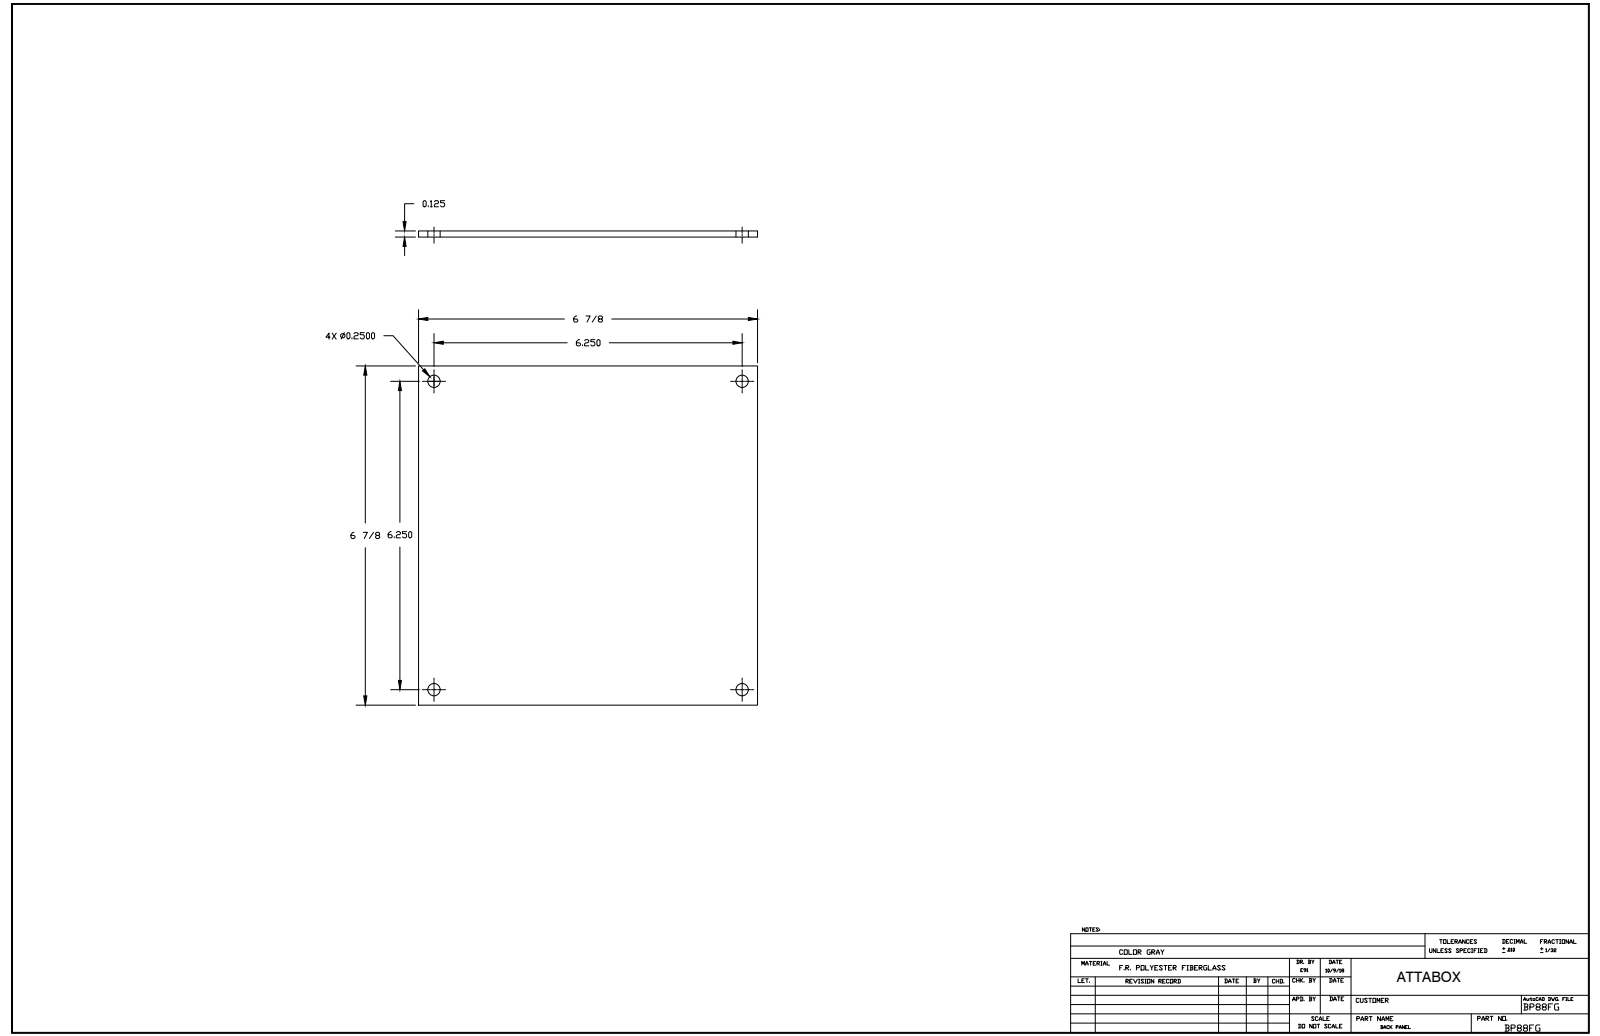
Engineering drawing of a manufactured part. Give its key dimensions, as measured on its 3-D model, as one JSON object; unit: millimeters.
{"part_name": "BP88FG_STP", "step_written_by": "Autodesk Inventor 2014 (AUTOMOTIVE_DESIGN)", "units": "millimeters", "bodies": {"solids": 1, "faces": 10, "planar": 6, "cylindrical": 4, "other": 0}, "overall_size": [174.62, 174.62, 3.17], "volume_mm3": 96416, "surface_area_mm2": 63206, "round_holes": [[6.35, 4]], "face_to_face_distances": [3.17, 174.62], "hole_center_spacings": [158.76, 224.52]}
